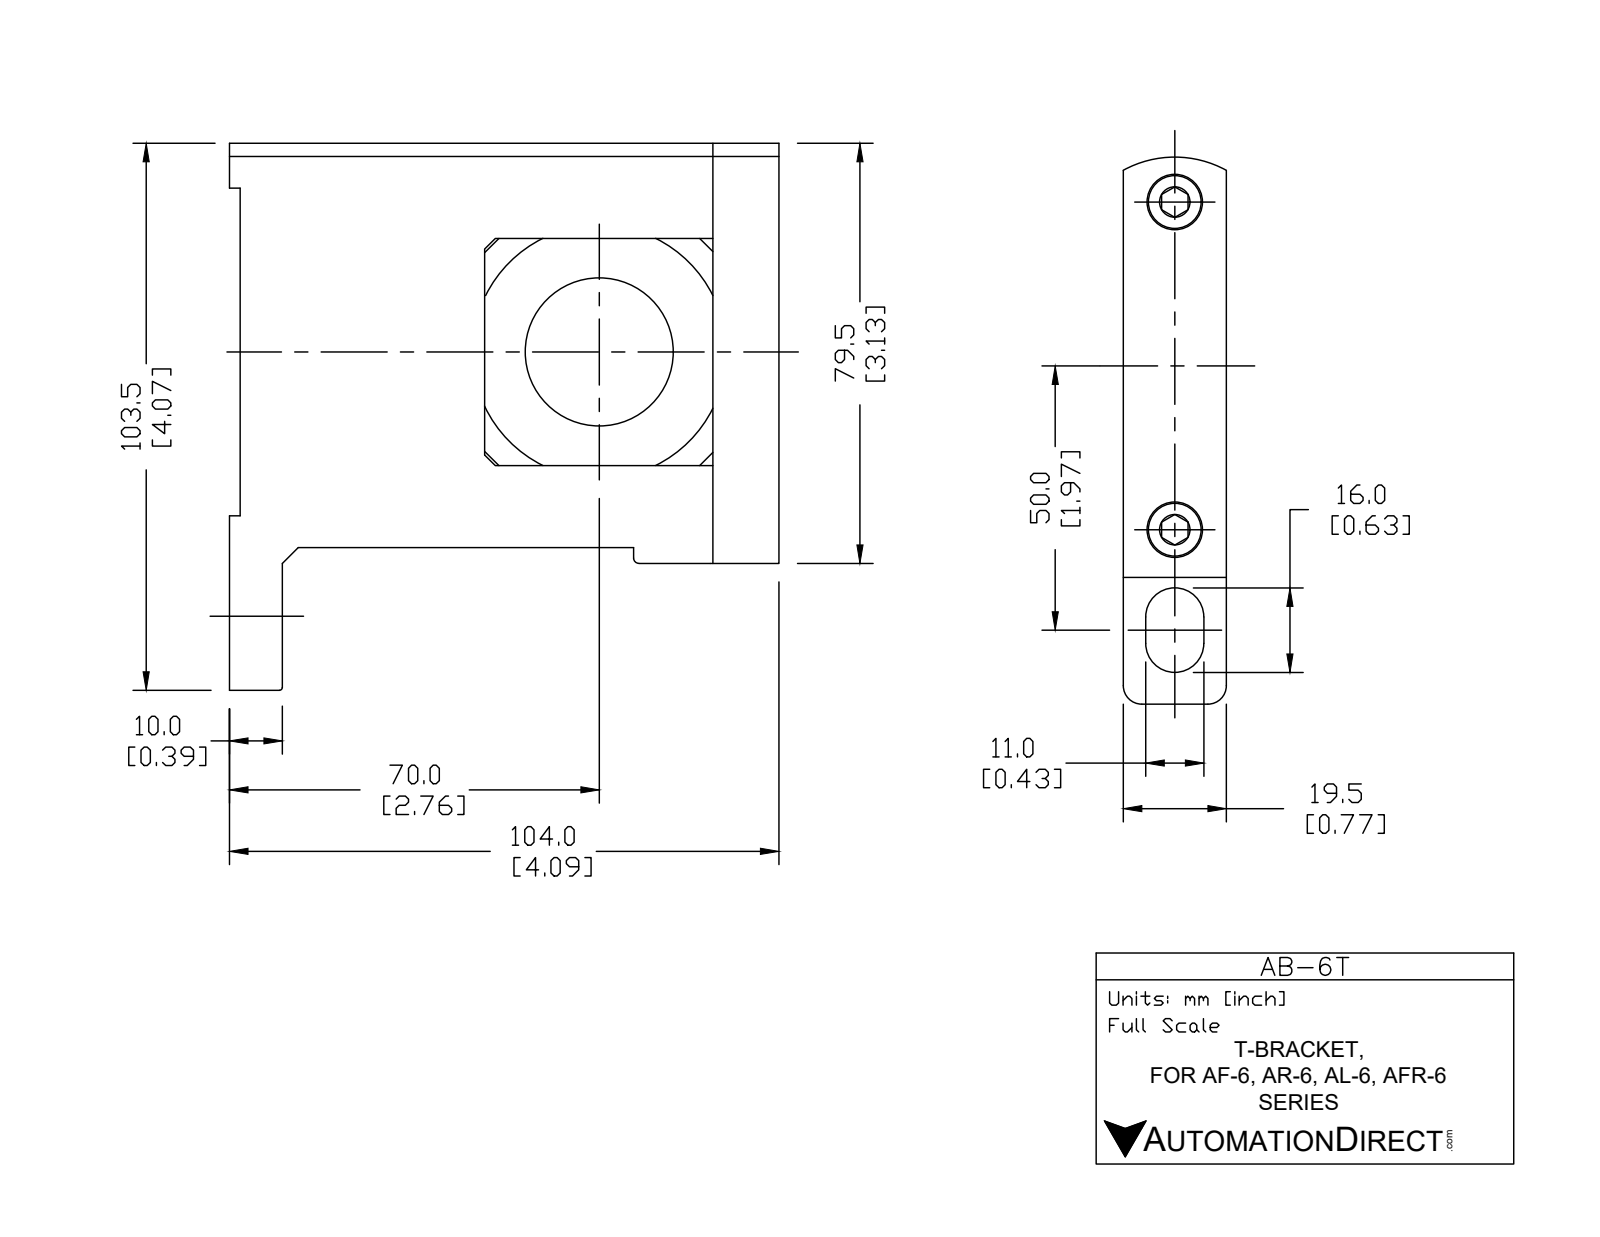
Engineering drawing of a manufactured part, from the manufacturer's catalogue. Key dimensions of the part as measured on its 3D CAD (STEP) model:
Part name (STEP PRODUCT): AB-6L
STEP written by: SolidWorks 2015 (CONFIG_CONTROL_DESIGN)
Units: millimetres
Bodies: 3 solids, 103 faces (69 planar, 22 cylindrical, 12 other)
Overall size (bounding box): 104 × 103.5 × 19.5
Volume: 118 948 mm³ · Surface area: 30 750 mm²
Round holes (diameter × count): ⌀6.5 ×2, ⌀10.53 ×2, ⌀28 ×1
Round bosses / shafts (diameter × count): ⌀9.75 ×2, ⌀4 ×2
Partial cylindrical surfaces — rounded edges, fillets, slot ends (radius × count): R5.5 ×2, R1.5 ×1, R20.26 ×1
Main face-to-face distances: 19.5, 3, 46, 102.25, 8.94, 10.56, 12.5, 3.75, 15.75, 5.19
Hole centre spacings: 62
